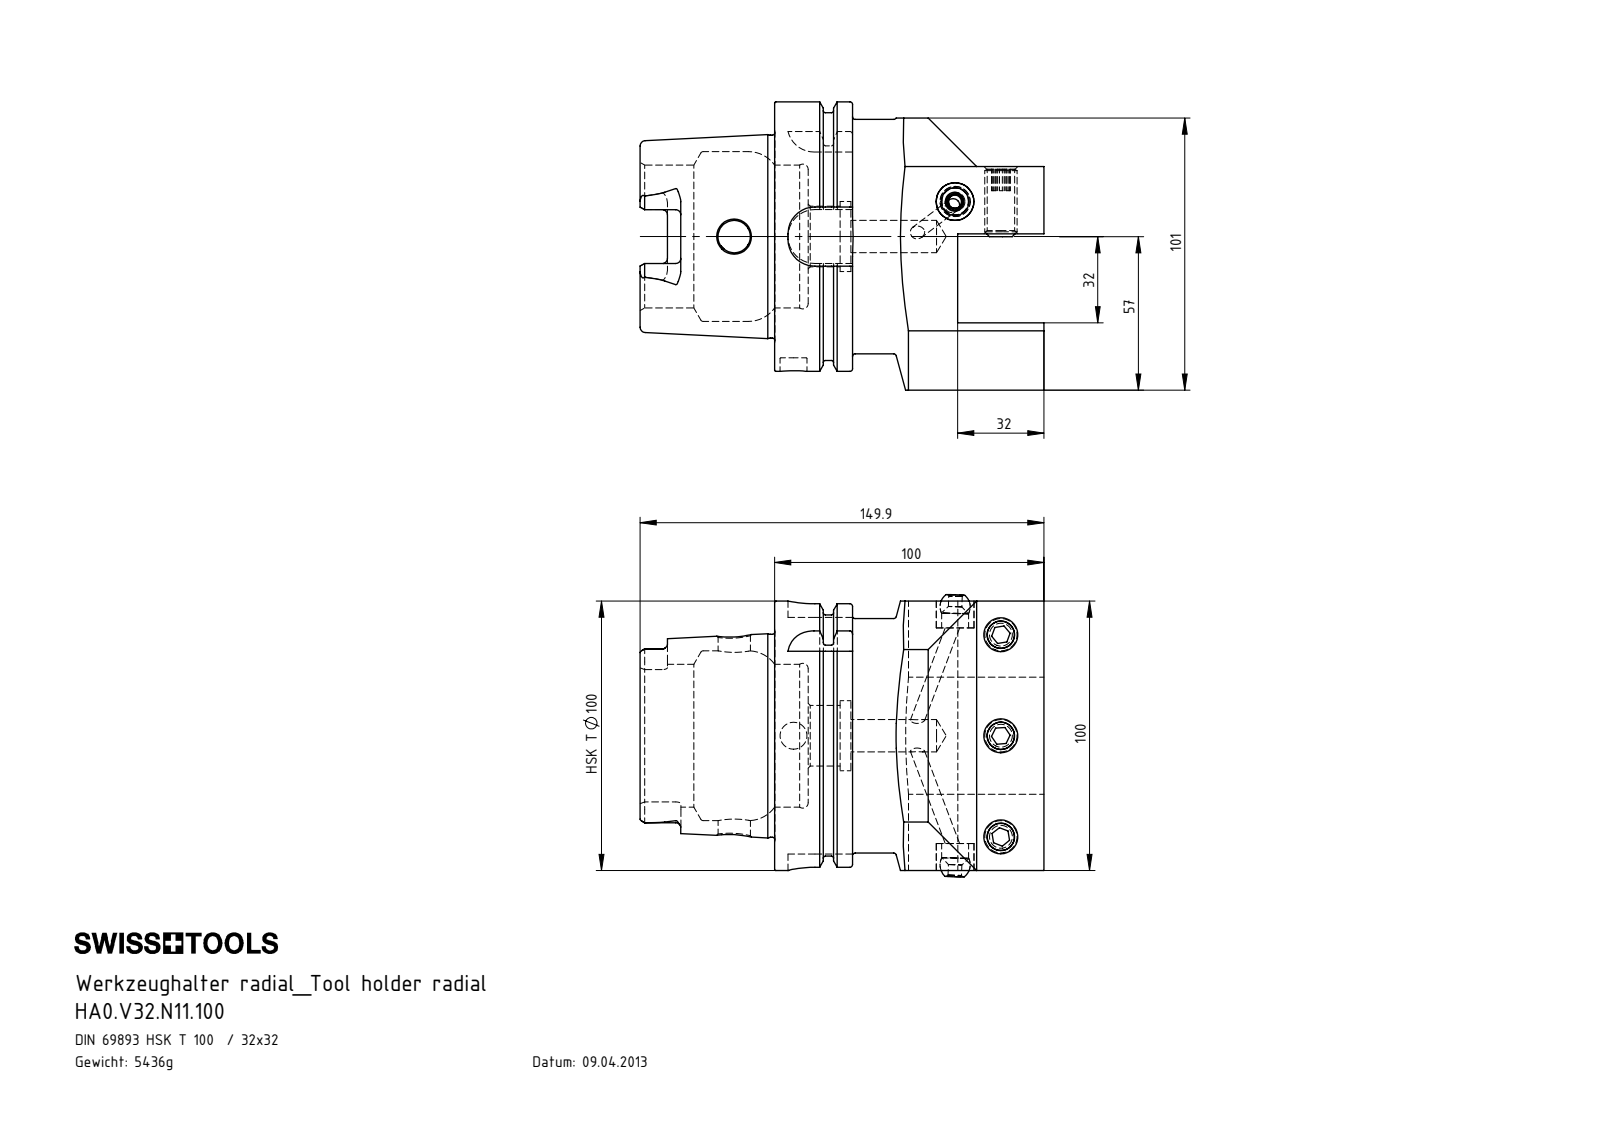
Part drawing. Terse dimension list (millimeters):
name: KU1-U14.001.012_1; HA0.V32.N11.100; ISO 4026 - M12 x 25; KU1-U14.001.012 (+2 more)
written by: SolidWorks 2017 (AUTOMOTIVE_DESIGN)
unit: mm
bodies: 8 solids, 201 faces (85 planar, 51 cylindrical, 65 other)
size: 149.9 × 107 × 105.63
volume: 693 473 mm³; area: 93 399 mm²
holes: 4× ⌀5, 3× ⌀10.2, 2× ⌀10, 2× ⌀12, 1× ⌀14, 1× ⌀22.5, 1× ⌀26, 1× ⌀53, 1× ⌀63
bosses: 3× ⌀12, 1× ⌀100, 1× ⌀91.95, 1× ⌀87, 1× ⌀75.26
rounds: 6× R1.9, 4× R4.88, 4× R10, 1× R0.8, 1× R61
face distances: 100, 25, 58, 32, 33, 68, 83, 12.45, 55.55, 87.55
hole spacings: 37.5, 85.65, 75, 77, 83.02
